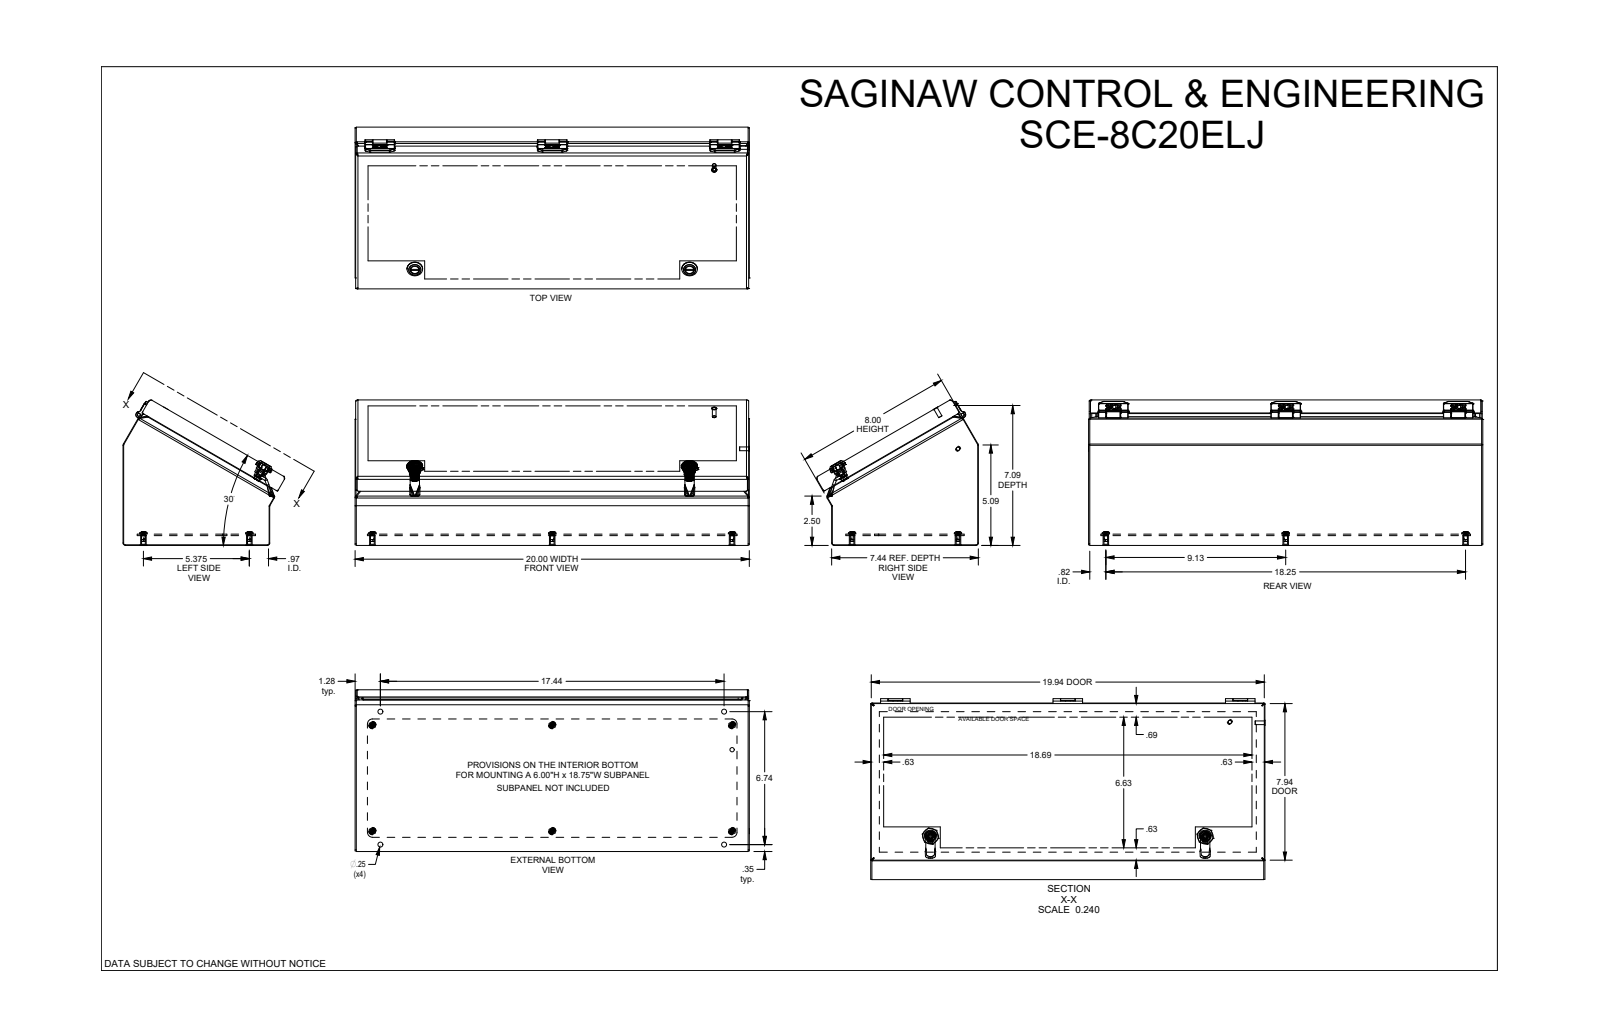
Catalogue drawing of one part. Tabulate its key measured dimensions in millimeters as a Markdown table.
| quantity | value |
| --- | --- |
| part name | SCE-8C20ELJ |
| STEP written by | SolidWorks 2019 (AUTOMOTIVE_DESIGN) |
| units | millimeters |
| bodies | 37 solids, 1464 faces (567 planar, 588 cylindrical, 309 other) |
| overall size | 508.1 × 208.3 × 187.5 |
| volume | 864 100 mm³ |
| surface area | 1 060 000 mm² |
| round holes (diameter × count) | 6.4 × 10, 4.8 × 6, 7.1 × 6, 0.5 × 3, 2.5 × 3, 4.4 × 3, 6.8 × 3, 4.9 × 2, 5.1 × 2, 6.1 × 2, 6.5 × 2, 6.8 × 2 |
| round bosses / shafts (diameter × count) | 7.1 × 6, 6.6 × 3, 4.6 × 3, 20 × 2, 13.9 × 2, 11.7 × 2, 10.9 × 2, 8.9 × 2 |
| partial cylindrical surfaces (radius × count) | 0.8 × 36, 0.3 × 31, 1.5 × 24, 0.3 × 22, 0.4 × 22, 3 × 16, 0.5 × 13, 1.6 × 9 |
| main face-to-face distances | 1.5, 1.5, 11.1, 12.6, 1.9, 13, 14.5, 187.5, 506.5, 189 |
| hole center spacings | 20.2, 154.2, 222.1, 222.3, 231.8, 269, 269.7, 354.1 |
